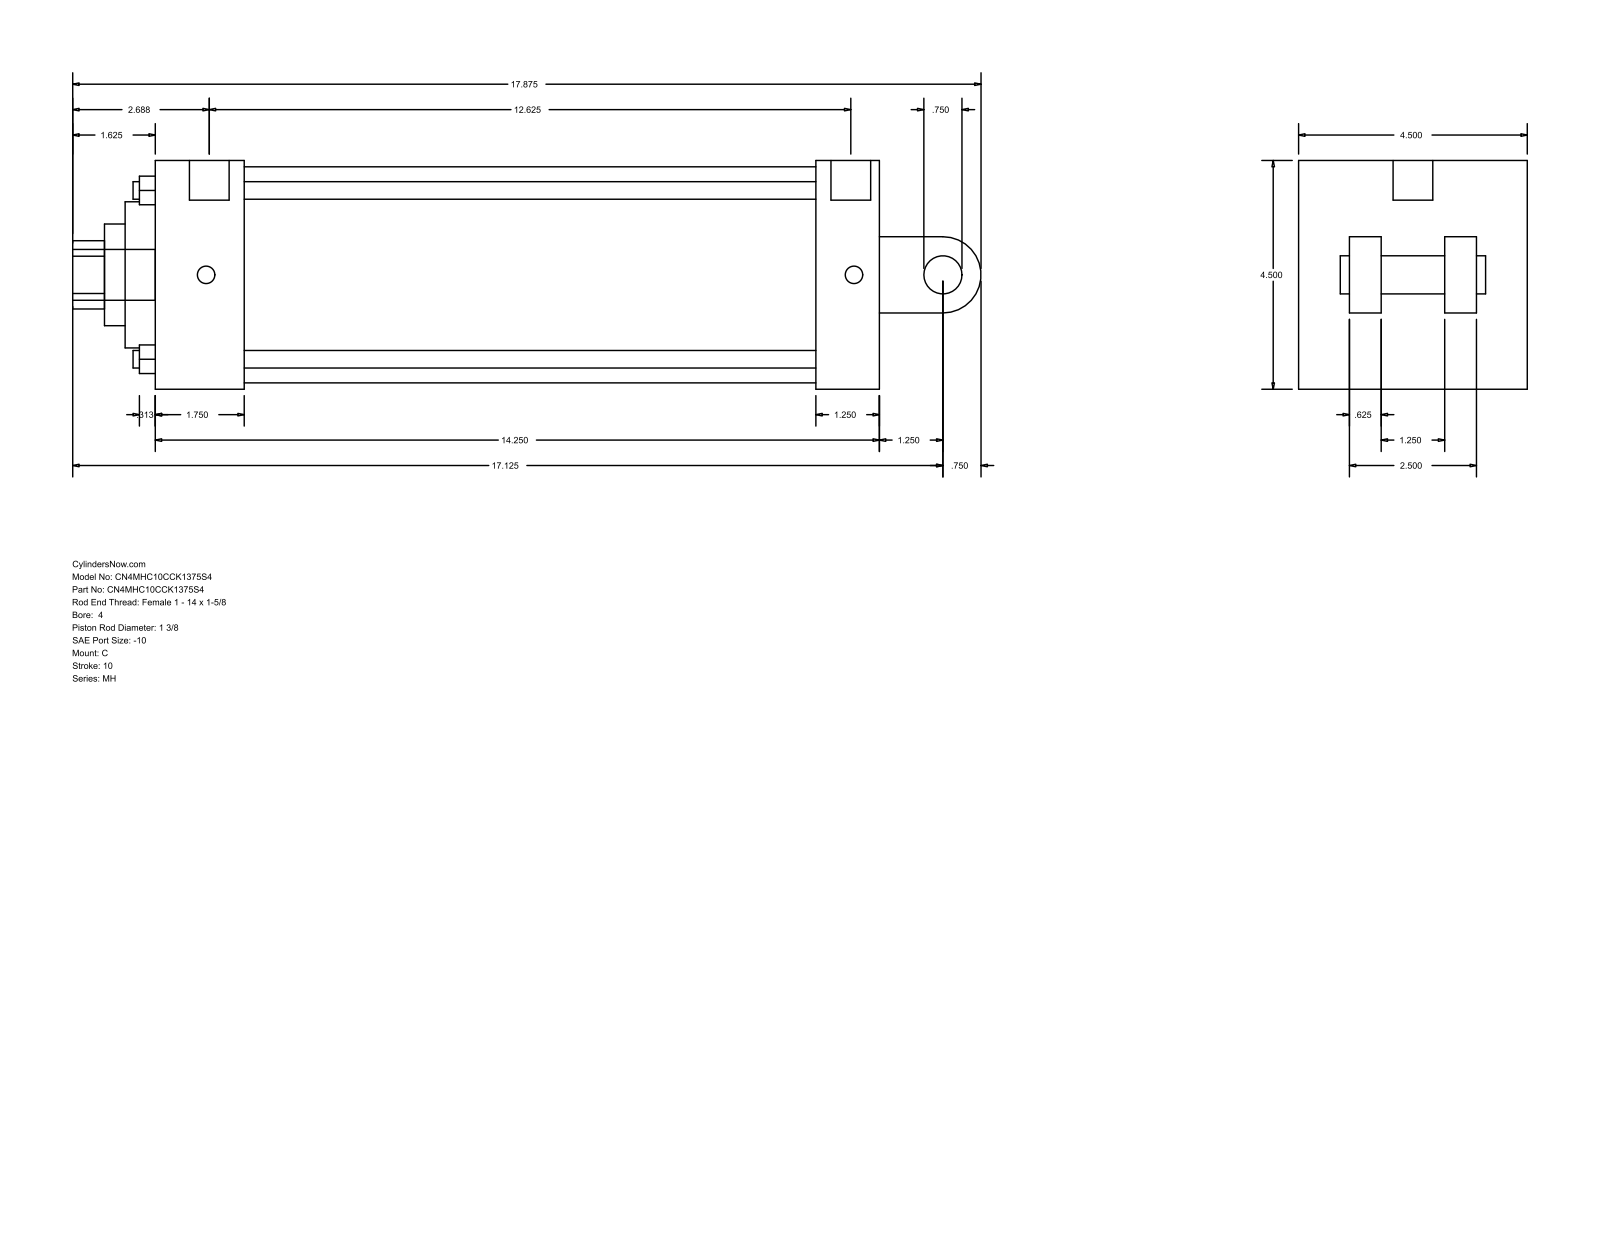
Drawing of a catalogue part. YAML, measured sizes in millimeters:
part_name: "MH_C__0400_1.375"
step_written_by: "GSSL Pune (CONFIG_CONTROL_DESIGN)"
units: millimeters
bodies: {solids: 0, faces: 101, planar: 71, cylindrical: 30, other: 0}
overall_size: [454.02, 114.3, 114.3]
round_holes:
  - {diameter: 8.76, count: 4}
  - {diameter: 8.73, count: 2}
  - {diameter: 19.84, count: 1}
  - {diameter: 34.92, count: 1}
  - {diameter: 50.8, count: 1}
  - {diameter: 73.03, count: 1}
  - {diameter: 107.95, count: 1}
round_bosses_or_shafts:
  - {diameter: 8.73, count: 2}
  - {diameter: 25.4, count: 1}
  - {diameter: 19.84, count: 1}
  - {diameter: 19.05, count: 1}
partial_cylinders:
  - {radius: 17.06, count: 1}
  - {radius: 19.05, count: 1}
face_to_face_distances: [114.3, 361.96, 44.45, 330.21, 285.76, 317.51, 31.75, 73.03, 41.27, 38.1]
hole_center_spacings: [59.62, 84.32, 119.25, 1.58]
